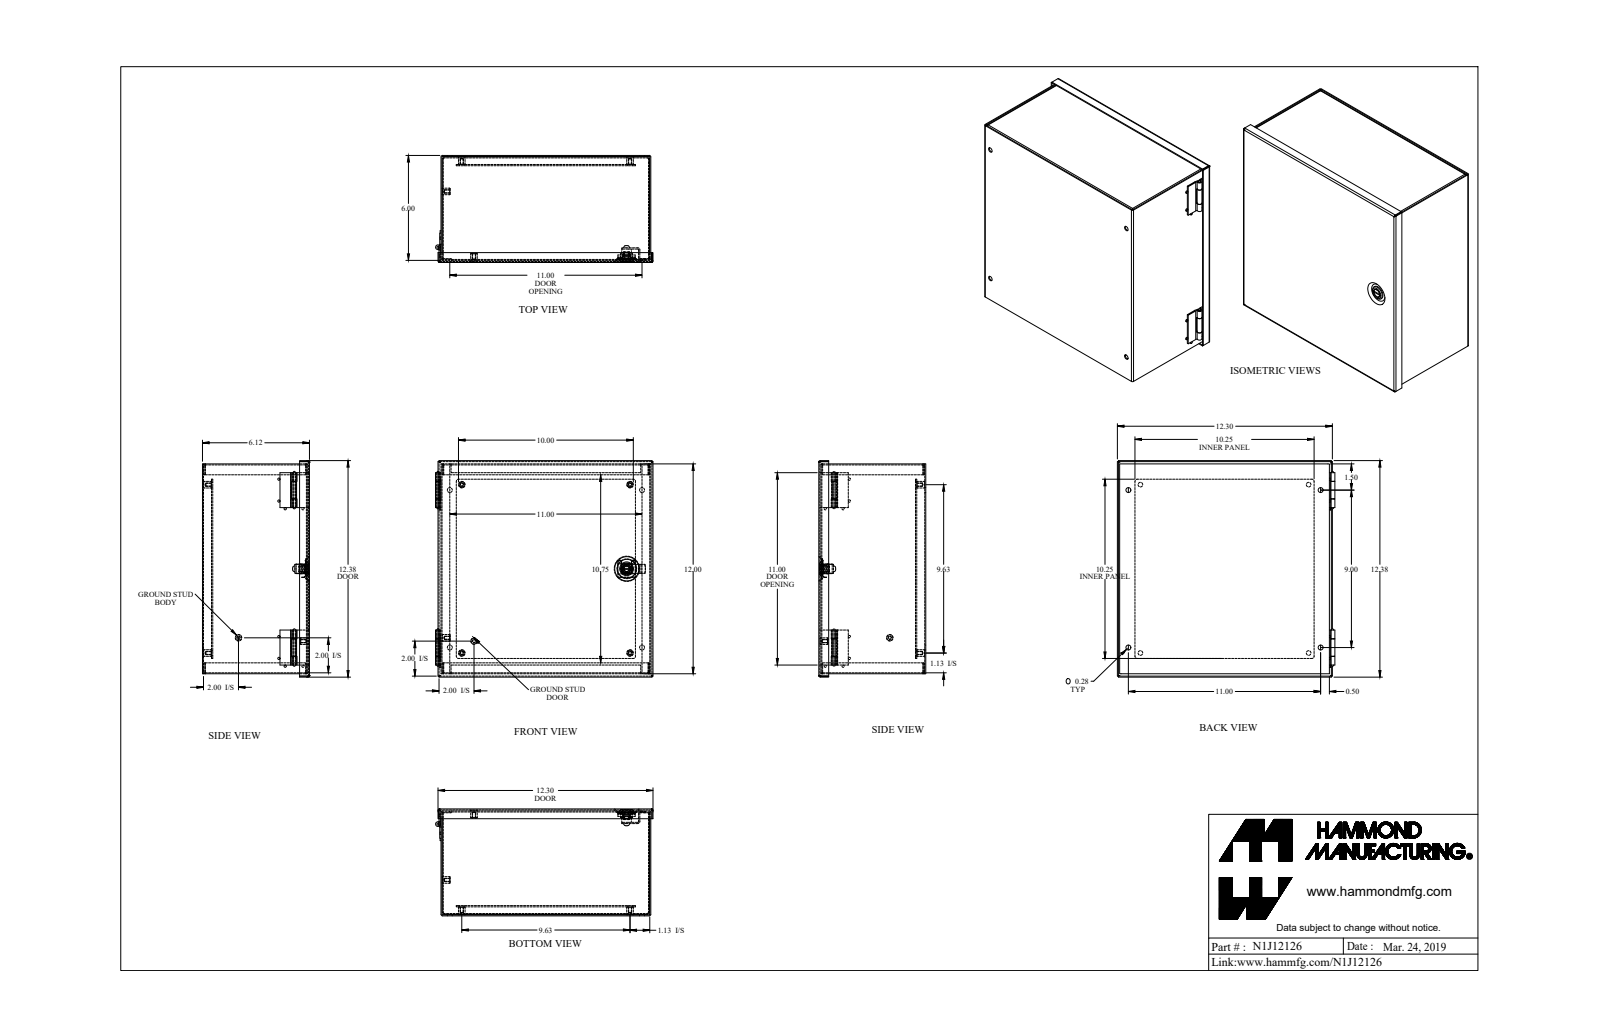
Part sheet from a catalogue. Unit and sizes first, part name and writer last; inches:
Units: inches
Overall size (bounding box): 12.443 × 12.38 × 6.118
Round holes (diameter × count): ⌀0.156 ×6, ⌀0.265 ×4, ⌀0.28 ×4, ⌀0.125 ×1, ⌀0.319 ×1, ⌀0.476 ×1
Round bosses / shafts (diameter × count): ⌀0.131 ×8, ⌀0.375 ×6, ⌀0.787 ×1, ⌀0.547 ×1, ⌀0.472 ×1, ⌀0.469 ×1, ⌀0.366 ×1, ⌀0.32 ×1
Partial cylindrical surfaces — rounded edges, fillets, slot ends (radius × count): R0.029 ×16, R0.086 ×16, R0.012 ×4, R0.1 ×4, R0.125 ×4, R0.036 ×2, R0.079 ×2, R0.25 ×2
Main face-to-face distances: 0.057, 6.061, 11.943, 6.004, 6.118, 12, 11.886, 0.072, 0.517, 0.46
Hole centre spacings: 0.755, 9.338, 9.625, 10.317, 13.895, 4.586, 4.817, 9
Volume: 45.58 in³ · Surface area: 1 550 in²
Bodies: 18 solids, 477 faces (224 planar, 188 cylindrical, 65 other)
Part name (STEP PRODUCT): N1J12126
STEP written by: SolidWorks 2018 (AUTOMOTIVE_DESIGN)
